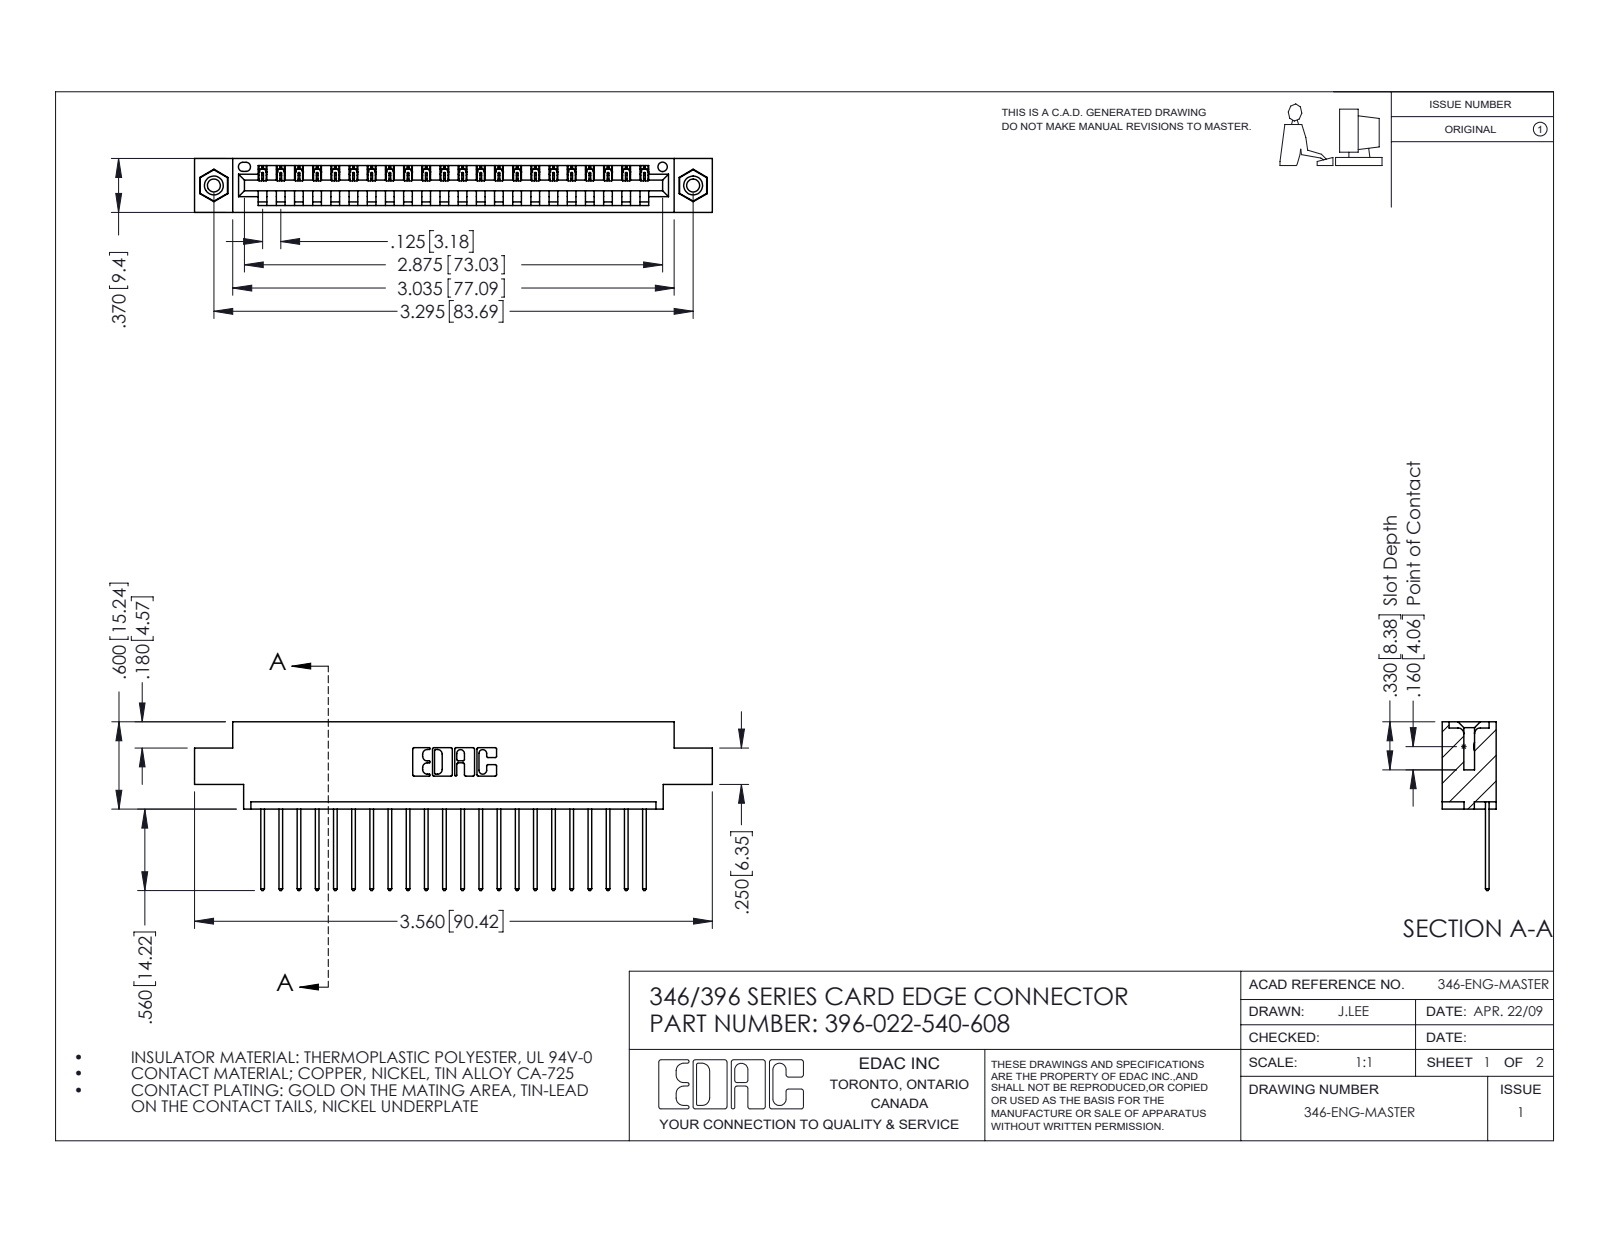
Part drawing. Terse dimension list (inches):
name: 345-250-001_345-250-003-102; 396-022-540-608; 345-292-001_345-293-140; 346 Part_0.170 Offset - 0.156 Dia-TI
written by: SolidWorks 2016 (CONFIG_CONTROL_DESIGN)
unit: in
bodies: 25 solids, 1462 faces (992 planar, 454 cylindrical, 16 other)
size: 3.56 × 1.16 × 0.37
volume: 0.512 in³; area: 16.53 in²
holes: 2× ⌀0.089, 2× ⌀0.125, 2× ⌀0.156, 1× ⌀0.064
bosses: 2× ⌀0.155
rounds: 44× R0.006, 44× R0.01, 22× R0.01, 6× R0.007, 6× R0.031, 3× R0.026, 2× R0.031, 2× R0.04
face distances: 0.048, 0.322, 0.37, 0.25, 0.072, 0.298, 0.025, 0.222, 0.148, 0.1
hole spacings: 0.246, 3.087, 3.295
